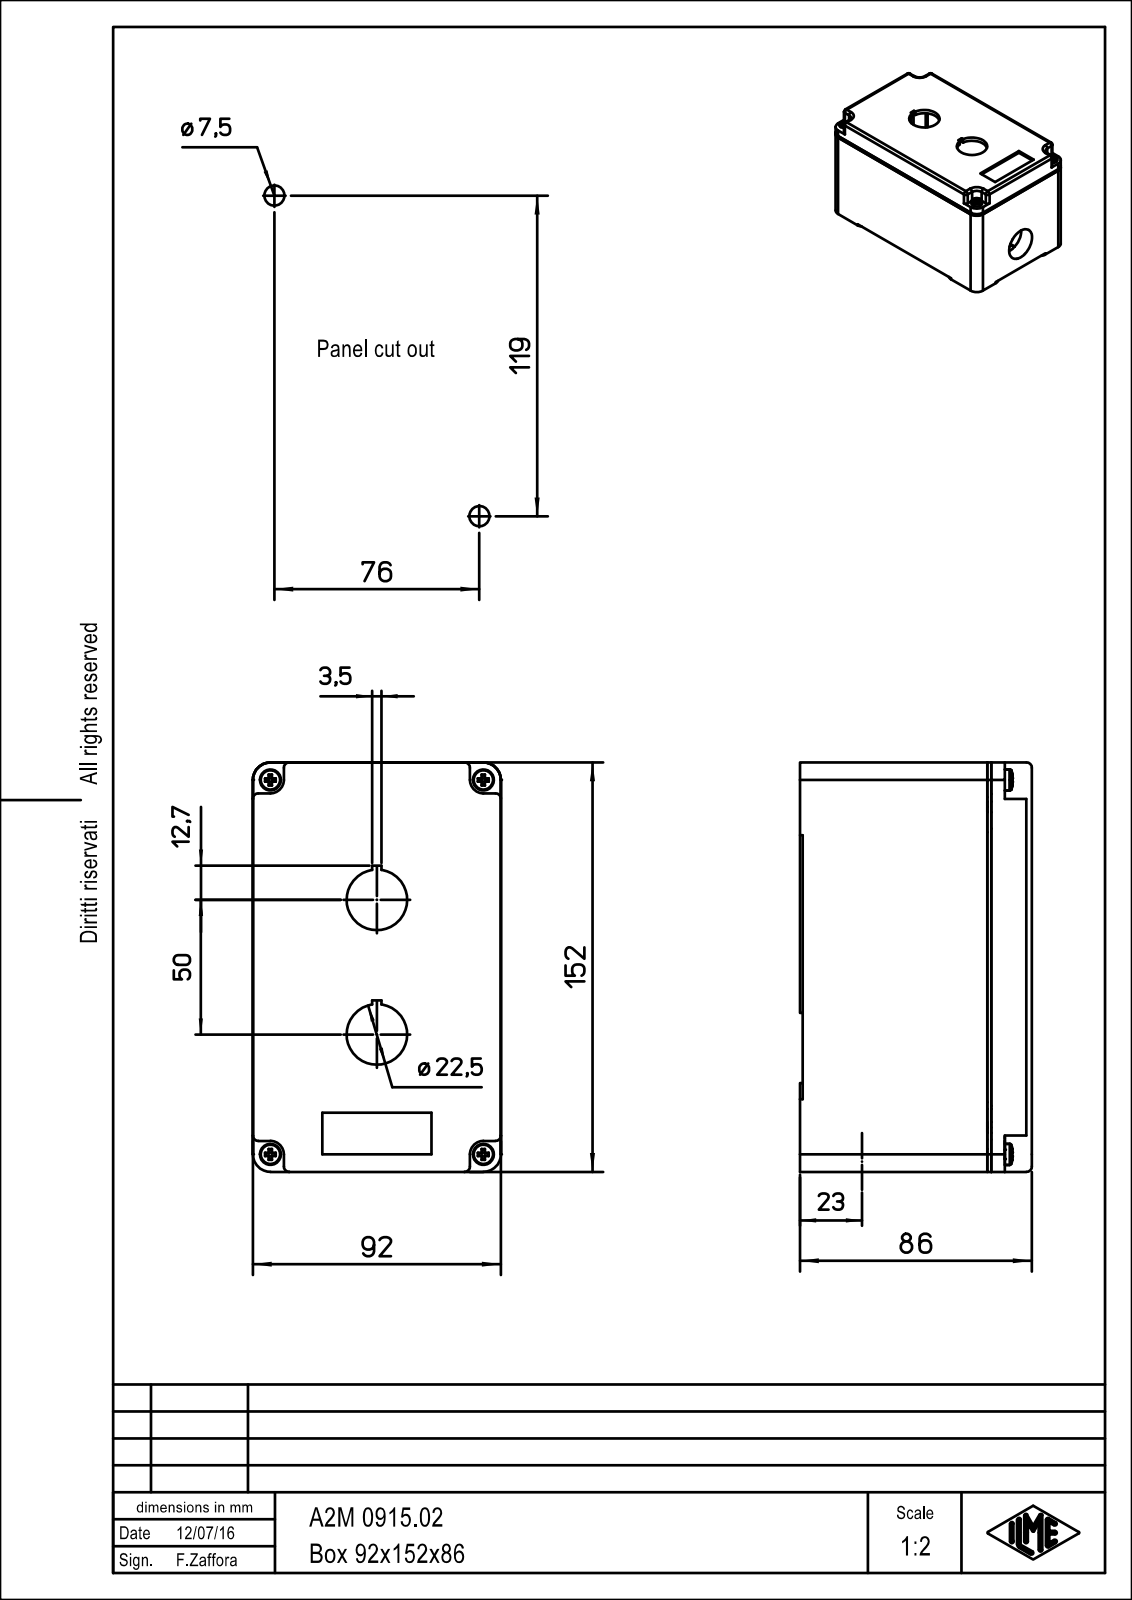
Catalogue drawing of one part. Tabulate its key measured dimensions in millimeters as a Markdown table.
| quantity | value |
| --- | --- |
| part name | COPERCHIO_C_0915.02; CASSETTA_B_0915; GUARNIZIONE_0915; VITE_M4X20 (+2 more) |
| STEP written by | Creo Elements/Direct Modeling 17.0C 05-Feb-2011 (C) Parametric Technology GmbH (AUTOMOTIVE_DESIGN) |
| units | millimeters |
| bodies | 9 solids, 1051 faces (799 planar, 212 cylindrical, 40 other) |
| overall size | 152 × 92 × 86 |
| volume | 281 611 mm³ |
| surface area | 155 309 mm² |
| round holes (diameter × count) | 3.3 × 6, 3.8 × 6, 4.5 × 4, 5 × 4, 6 × 4, 5.8 × 2, 7.5 × 2, 22.5 × 2, 10.6 × 1, 10.61 × 1, 25.4 × 1 |
| round bosses / shafts (diameter × count) | 4 × 7, 7.8 × 4, 3.5 × 4, 6.2 × 2, 6 × 2, 7 × 1 |
| partial cylindrical surfaces (radius × count) | 0.33 × 22, 2 × 16, 6 × 12, 6.5 × 8, 5 × 6, 8 × 6, 0.27 × 4, 0.27 × 4 |
| main face-to-face distances | 3, 82, 92, 4.38, 4.37, 85, 79, 1.5, 13.5, 65.5 |
| hole center spacings | 79, 59.5, 78.14, 102.42, 139, 159.88, 10.11, 11.67 |
